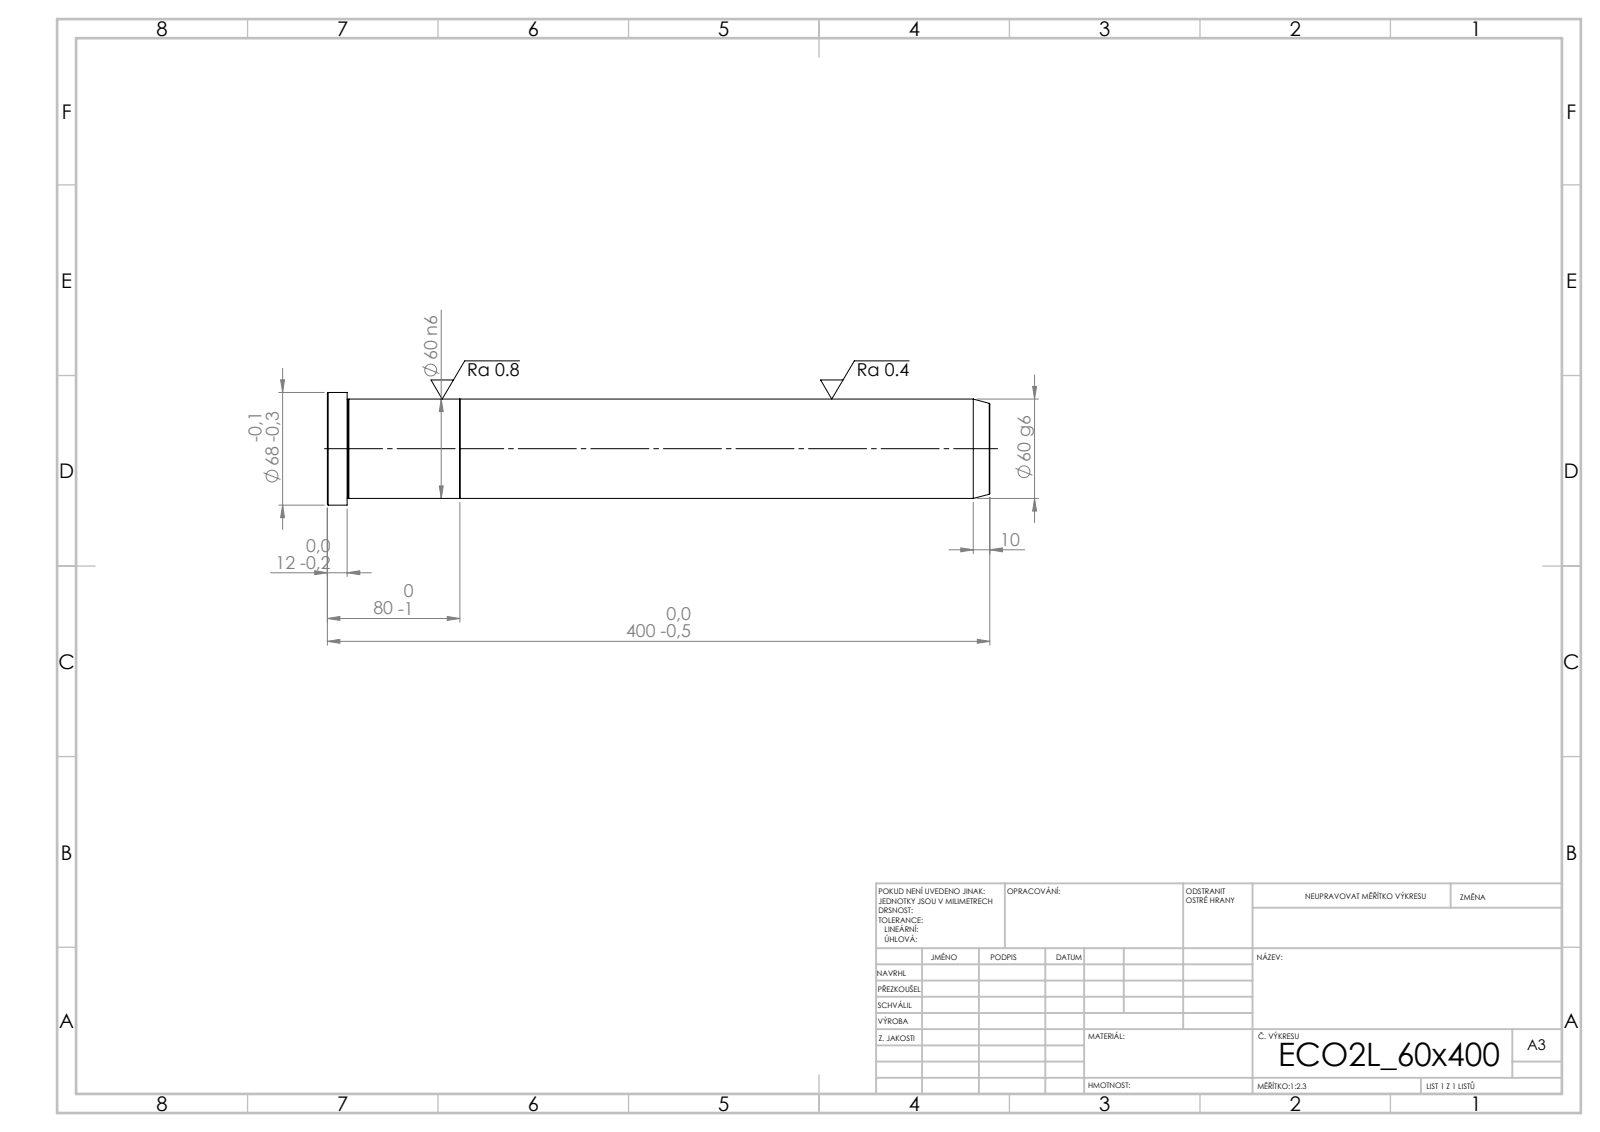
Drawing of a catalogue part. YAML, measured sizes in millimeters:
step_written_by: "SolidWorks 2019 (CONFIG_CONTROL_DESIGN)"
units: millimeters
bodies: {solids: 2, faces: 21, planar: 5, cylindrical: 6, other: 10}
overall_size: [400, 68, 68]
volume: 1138000
surface_area: 88137
round_bosses_or_shafts:
  - {diameter: 68, count: 1}
  - {diameter: 60, count: 1}
face_to_face_distances: [80, 320, 400, 388, 68, 12]
